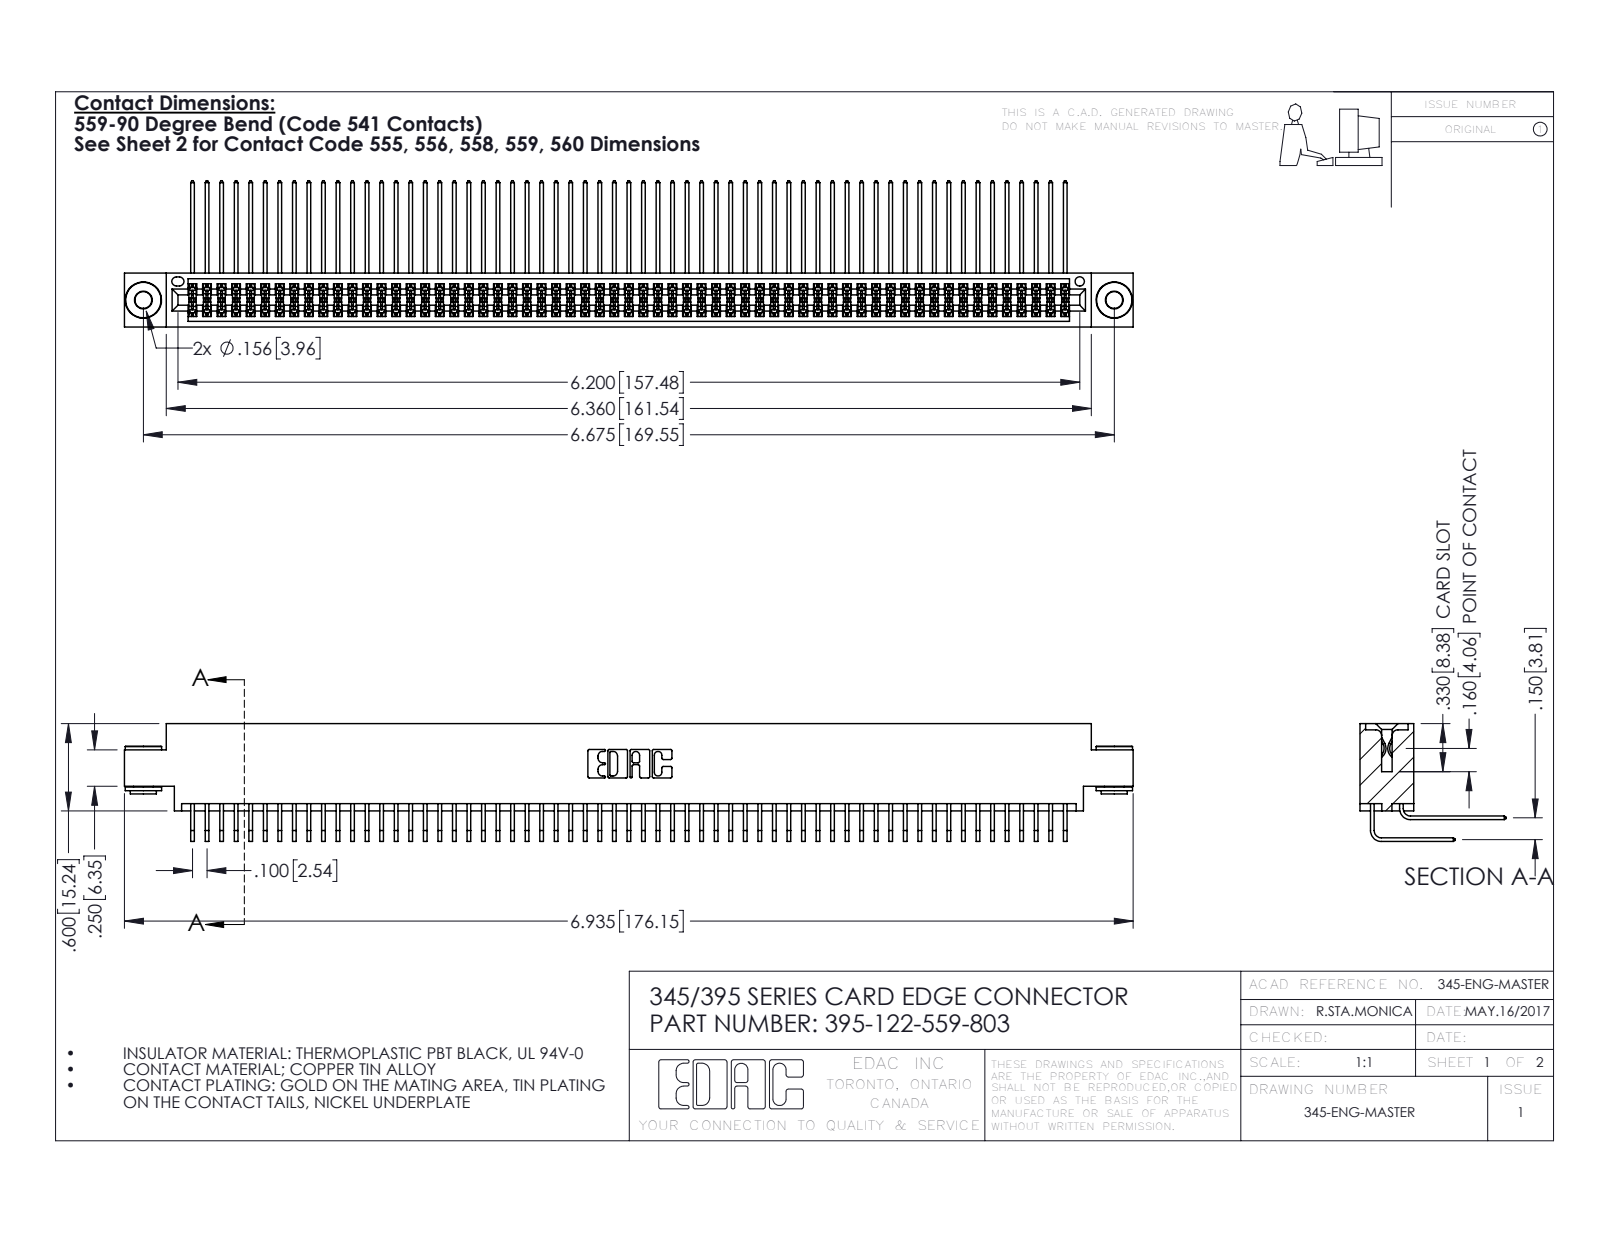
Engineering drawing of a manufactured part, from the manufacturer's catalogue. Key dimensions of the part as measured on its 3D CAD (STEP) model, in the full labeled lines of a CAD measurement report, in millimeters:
Part name (STEP PRODUCT): 345 Part_0.170 Offset - 0.156 Dia-TH; 345-292-001_559 Tail - 2; 345-292-001_558 559 Tail - 1; 345-250-002_345-250-002-102 (+1 more)
STEP written by: SolidWorks 2016 (CONFIG_CONTROL_DESIGN)
Units: millimetres
Bodies: 125 solids, 6512 faces (4364 planar, 2140 cylindrical, 8 other)
Overall size (bounding box): 176.1 × 25.5 × 20.5
Volume: 17 890 mm³ · Surface area: 30 480 mm²
Round holes (diameter × count): ⌀2.9 ×2, ⌀4 ×2, ⌀1.6 ×1
Round bosses / shafts (diameter × count): ⌀6.4 ×2, ⌀4.6 ×2, ⌀3.5 ×2
Partial cylindrical surfaces — rounded edges, fillets, slot ends (radius × count): R0.2 ×183, R0.3 ×22, R0.2 ×6, R0.8 ×6, R0.7 ×3, R0.4 ×2, R0.5 ×2, R0.6 ×2
Main face-to-face distances: 1.8, 7.6, 9.4, 5.1, 2.5, 6.9, 0.6, 5.7, 4.4, 3.8
Hole centre spacings: 6.9, 163.6, 169.5
